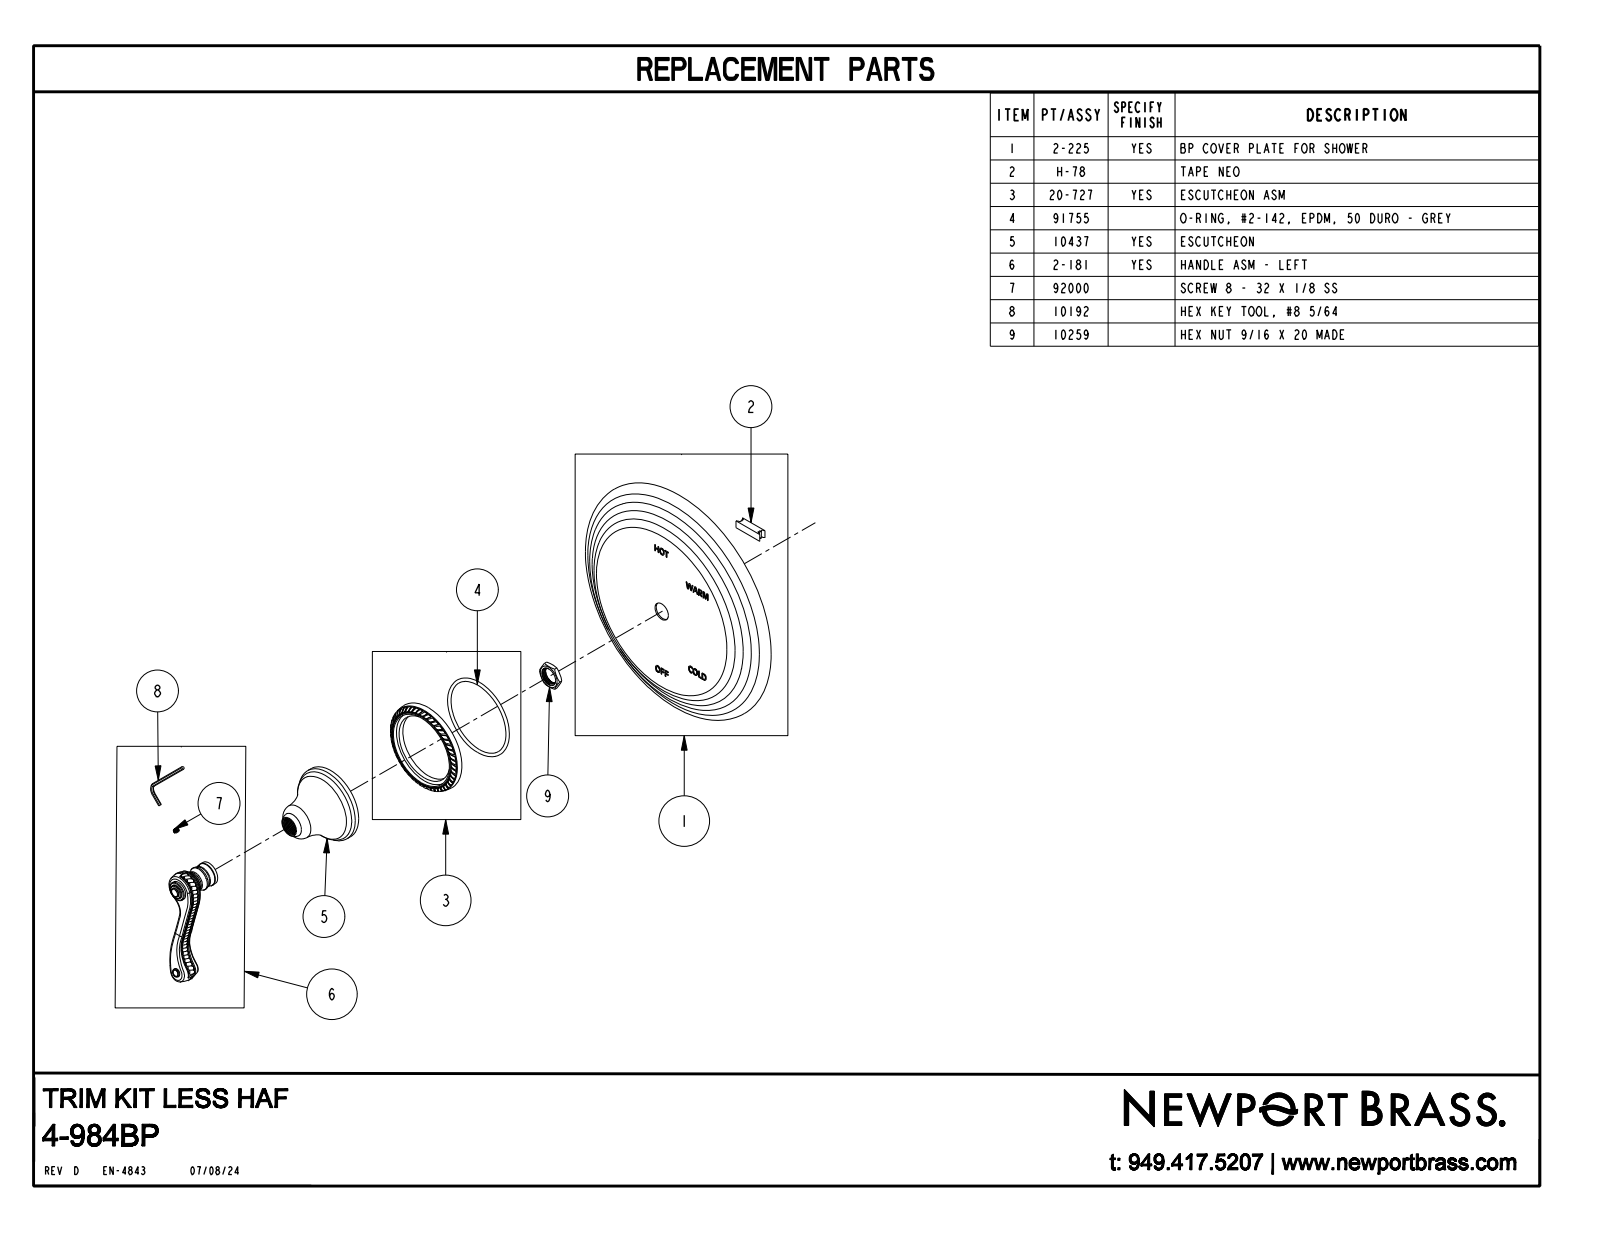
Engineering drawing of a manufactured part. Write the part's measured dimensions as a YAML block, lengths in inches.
part_name: "4-984BP"
step_written_by: "CREO PARAMETRIC BY PTC INC, 2018400 (CONFIG_CONTROL_DESIGN)"
units: inches
bodies: {solids: 1, faces: 767, planar: 235, cylindrical: 120, other: 412}
overall_size: [7.75, 7.75, 4.154]
volume: 33.57
surface_area: 118.1
round_bosses_or_shafts:
  - {diameter: 0.26, count: 2}
  - {diameter: 2.35, count: 1}
  - {diameter: 0.73, count: 1}
  - {diameter: 0.7, count: 1}
  - {diameter: 0.6, count: 1}
  - {diameter: 0.44, count: 1}
  - {diameter: 0.4, count: 1}
  - {diameter: 0.29, count: 1}
partial_cylinders:
  - {radius: 0.15, count: 49}
  - {radius: 0.09, count: 25}
  - {radius: 0.12, count: 24}
  - {radius: 11, count: 2}
  - {radius: 0.121, count: 1}
  - {radius: 0.137, count: 1}
face_to_face_distances: [0.754, 3.984, 3.23, 3.494, 2.74, 0.49, 1.044, 0.29, 2.45, 2.94]
